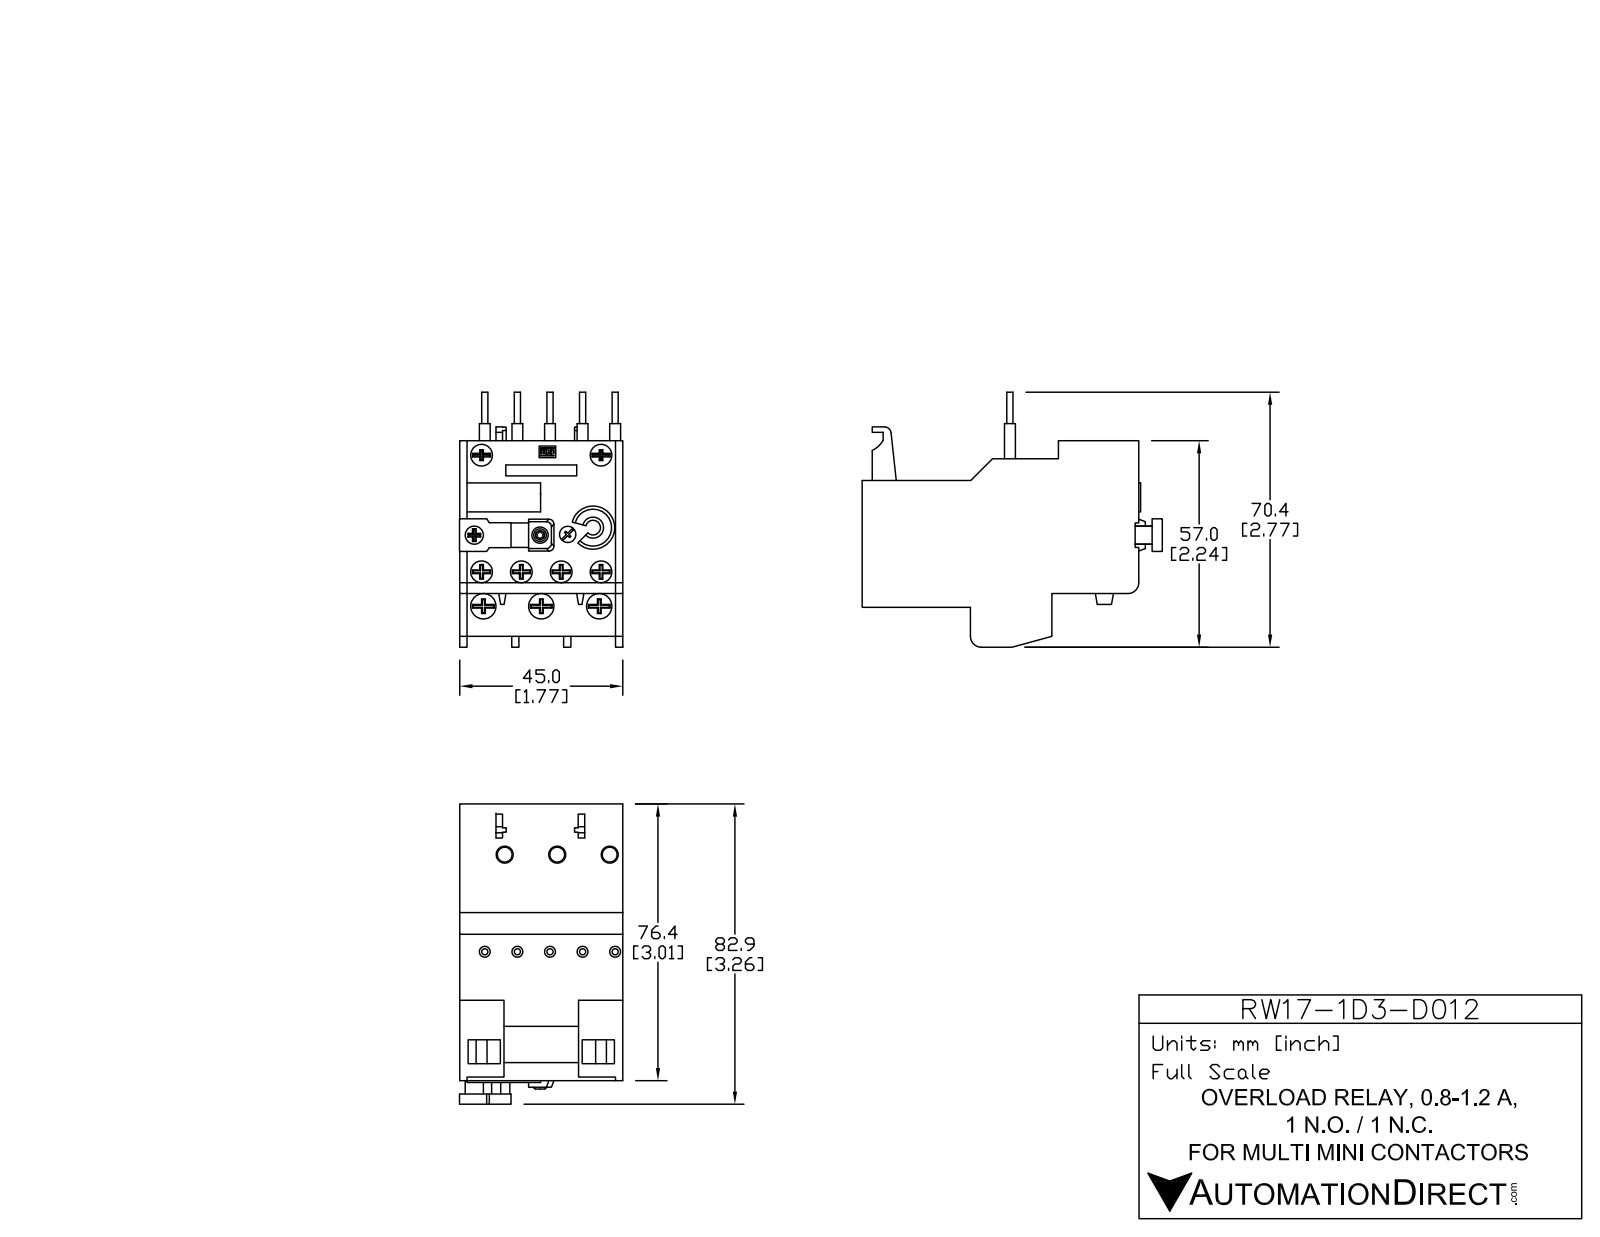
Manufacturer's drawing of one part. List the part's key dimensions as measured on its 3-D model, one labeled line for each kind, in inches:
Part name (STEP PRODUCT): RW17D-1D3-D012
STEP written by: SolidWorks 2013 (AUTOMOTIVE_DESIGN)
Units: inches
Bodies: 18 solids, 756 faces (515 planar, 214 cylindrical, 27 other)
Overall size (bounding box): 3.254 × 2.776 × 1.793
Volume: 7.778 in³ · Surface area: 53.79 in²
Round holes (diameter × count): ⌀0.236 ×6, ⌀0.157 ×3, ⌀0.276 ×3, ⌀0.295 ×3, ⌀0.177 ×1, ⌀0.187 ×1, ⌀0.21 ×1, ⌀0.217 ×1, ⌀0.41 ×1
Round bosses / shafts (diameter × count): ⌀0.217 ×7, ⌀0.118 ×7, ⌀0.069 ×5, ⌀0.22 ×2, ⌀0.128 ×2, ⌀0.253 ×1, ⌀0.242 ×1, ⌀0.187 ×1
Partial cylindrical surfaces — rounded edges, fillets, slot ends (radius × count): R0.02 ×20, R0.01 ×12, R0.039 ×9, R0.178 ×6, R0.231 ×4, R0.309 ×4, R0.059 ×3, R0.049 ×2
Main face-to-face distances: 1.791, 0.059, 0.427, 0.433, 3.008, 1.378, 0.056, 2.952, 2.949, 0.236
Hole centre spacings: 0.591, 0.337, 0.423, 1.181, 0.416, 0.467, 0.561, 0.841
